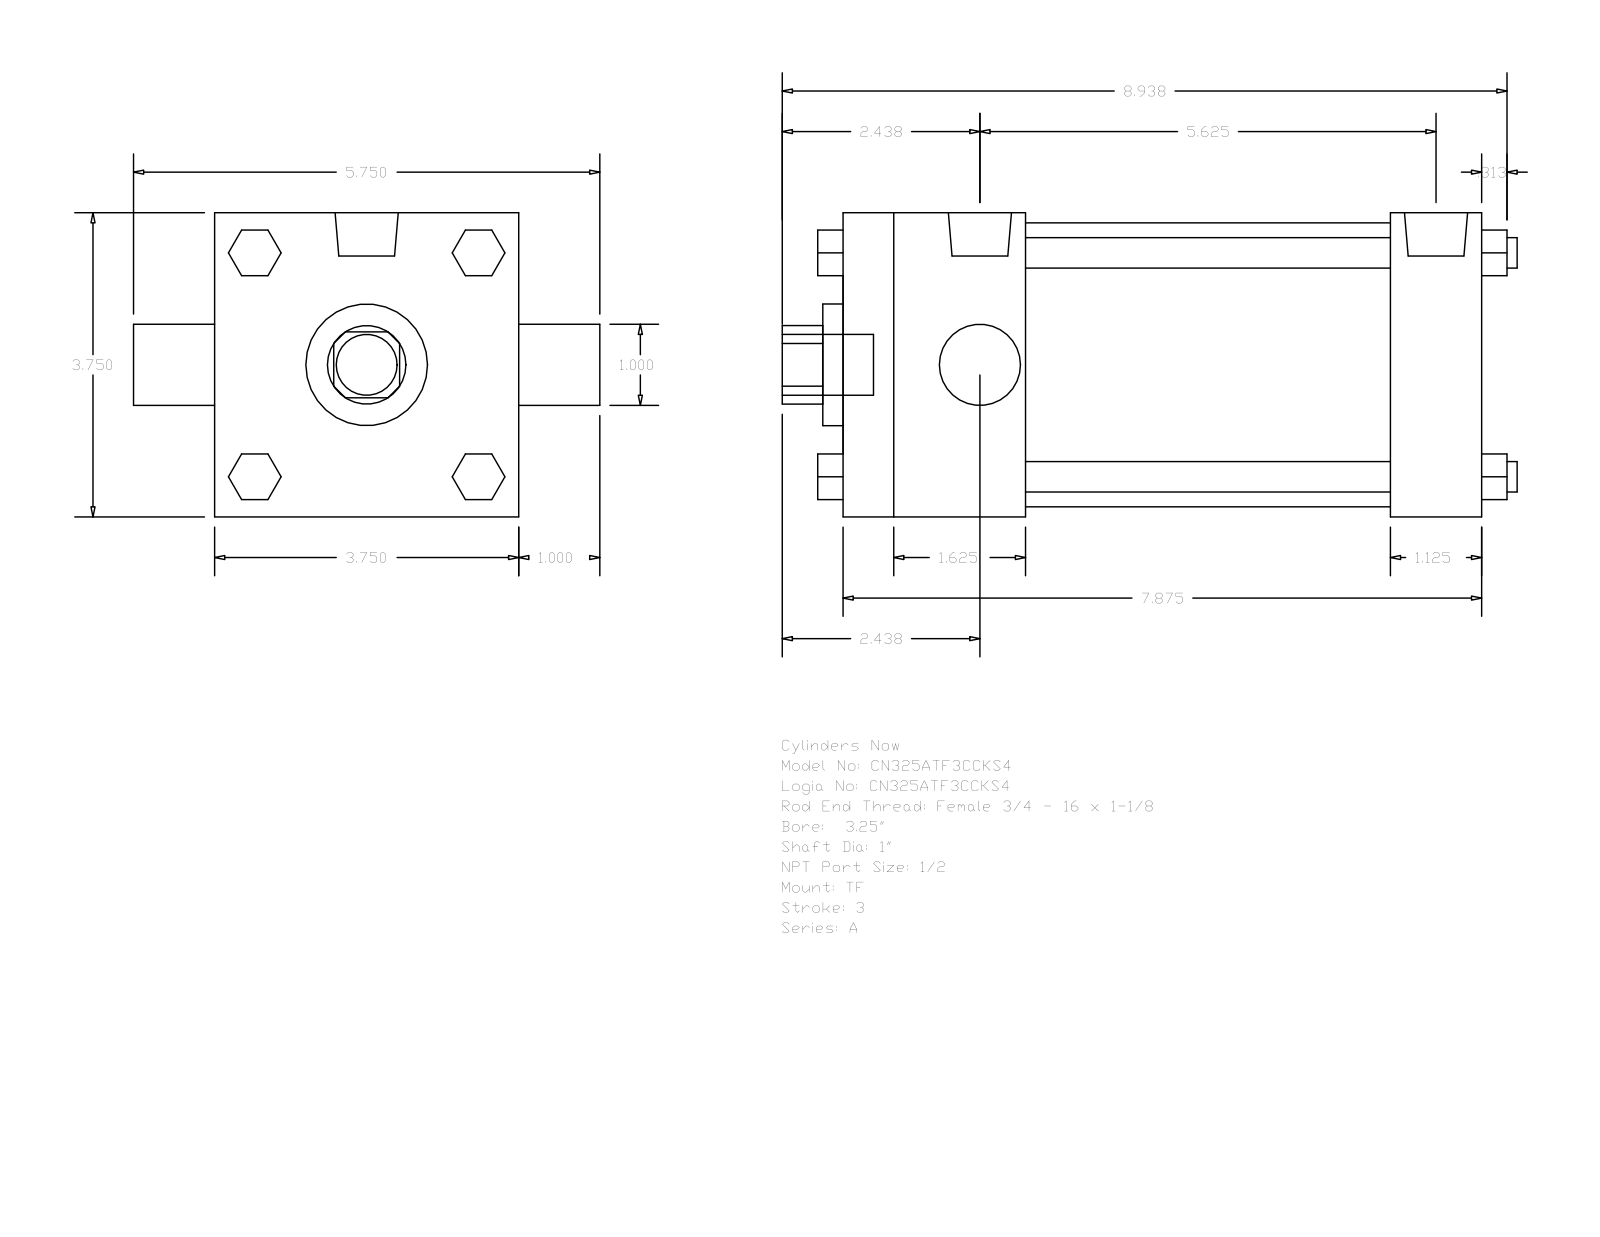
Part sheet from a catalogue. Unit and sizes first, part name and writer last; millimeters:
Units: millimetres
Overall size (bounding box): 230.19 × 146.05 × 95.25
Round holes (diameter × count): ⌀25.4 ×2, ⌀38.1 ×1, ⌀88.9 ×1
Round bosses / shafts (diameter × count): ⌀9.53 ×4, ⌀8.73 ×3, ⌀19.77 ×2, ⌀19.05 ×1
Partial cylindrical surfaces — rounded edges, fillets, slot ends (radius × count): R12.29 ×1
Main face-to-face distances: 95.24, 200.02, 28.57, 57.15, 171.45, 114.3, 142.87, 14.28, 35.05, 60.71
Bodies: 0 solids, 120 faces (92 planar, 28 cylindrical, 0 other)
Part name (STEP PRODUCT): A_TF__0325_1
STEP written by: GSSL Pune (CONFIG_CONTROL_DESIGN)
